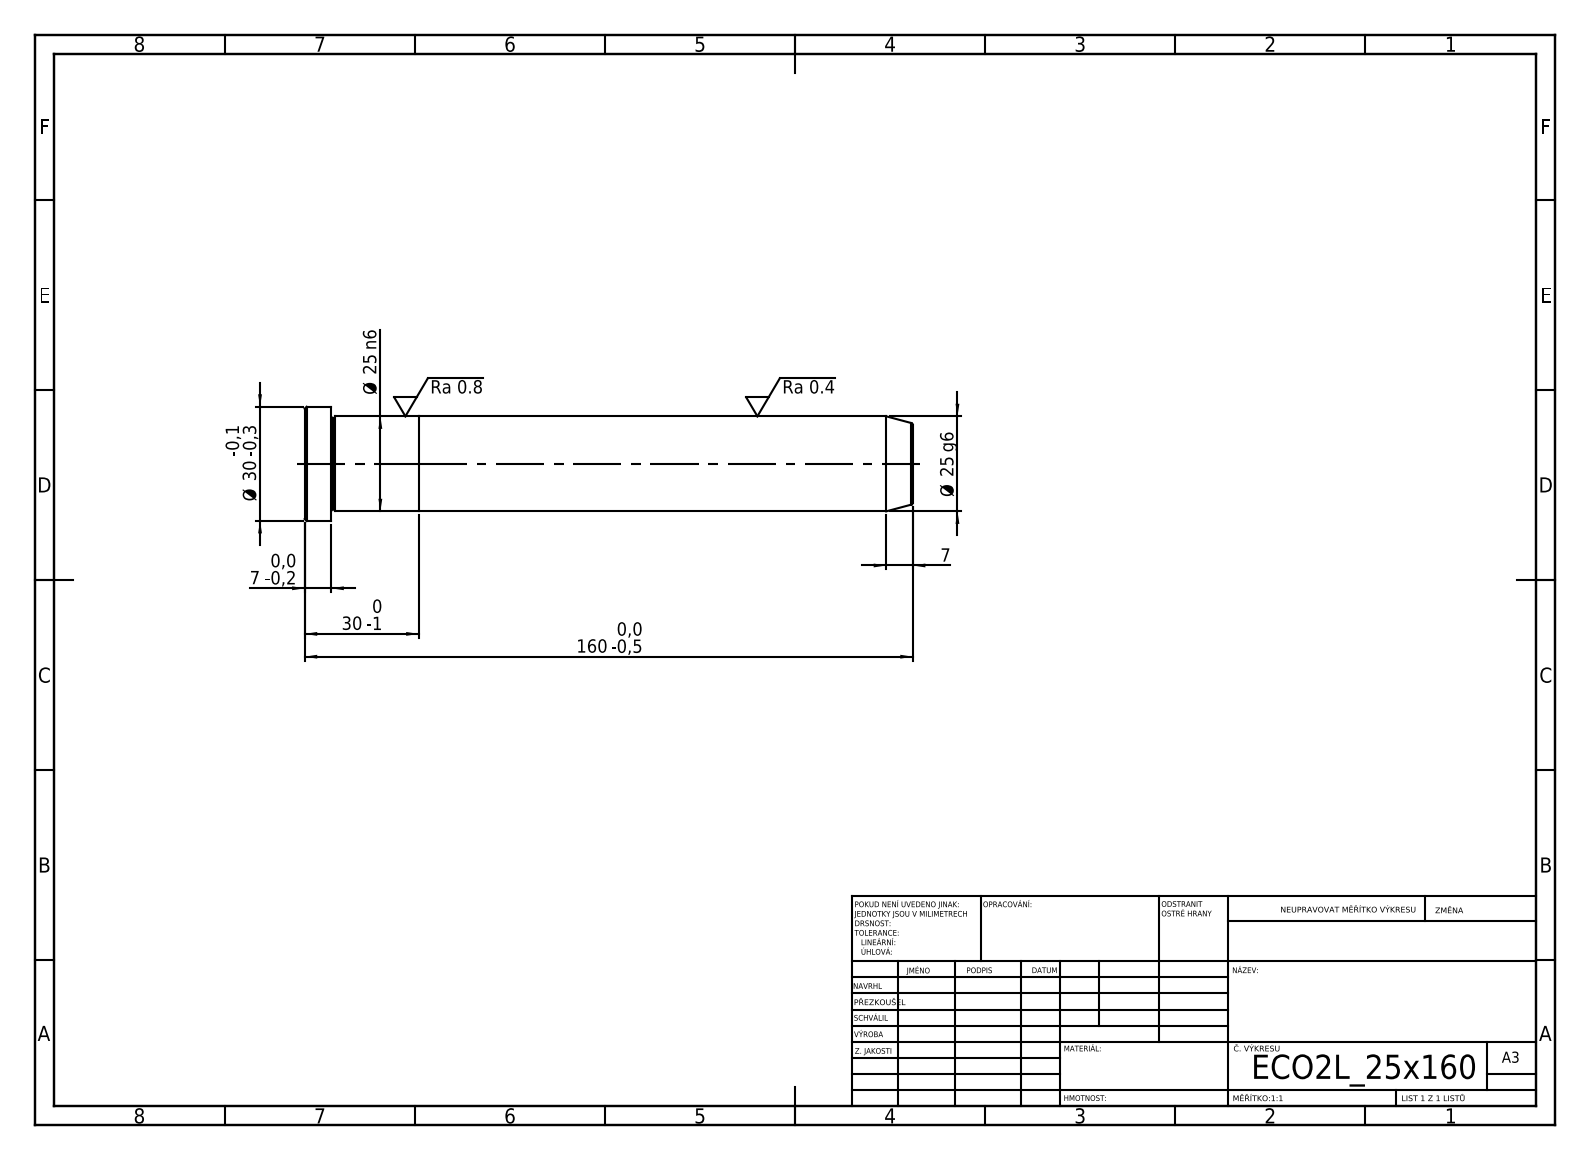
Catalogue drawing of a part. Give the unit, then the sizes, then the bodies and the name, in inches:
Units: inches
Overall size (bounding box): 6.299 × 1.181 × 1.181
Round bosses / shafts (diameter × count): ⌀1.181 ×1, ⌀0.984 ×1
Main face-to-face distances: 1.181, 5.118, 6.299, 6.024, 0.906, 0.276
Volume: 4.852 in³ · Surface area: 23.12 in²
Bodies: 2 solids, 21 faces (5 planar, 6 cylindrical, 10 other)
STEP written by: SolidWorks 2019 (CONFIG_CONTROL_DESIGN)
